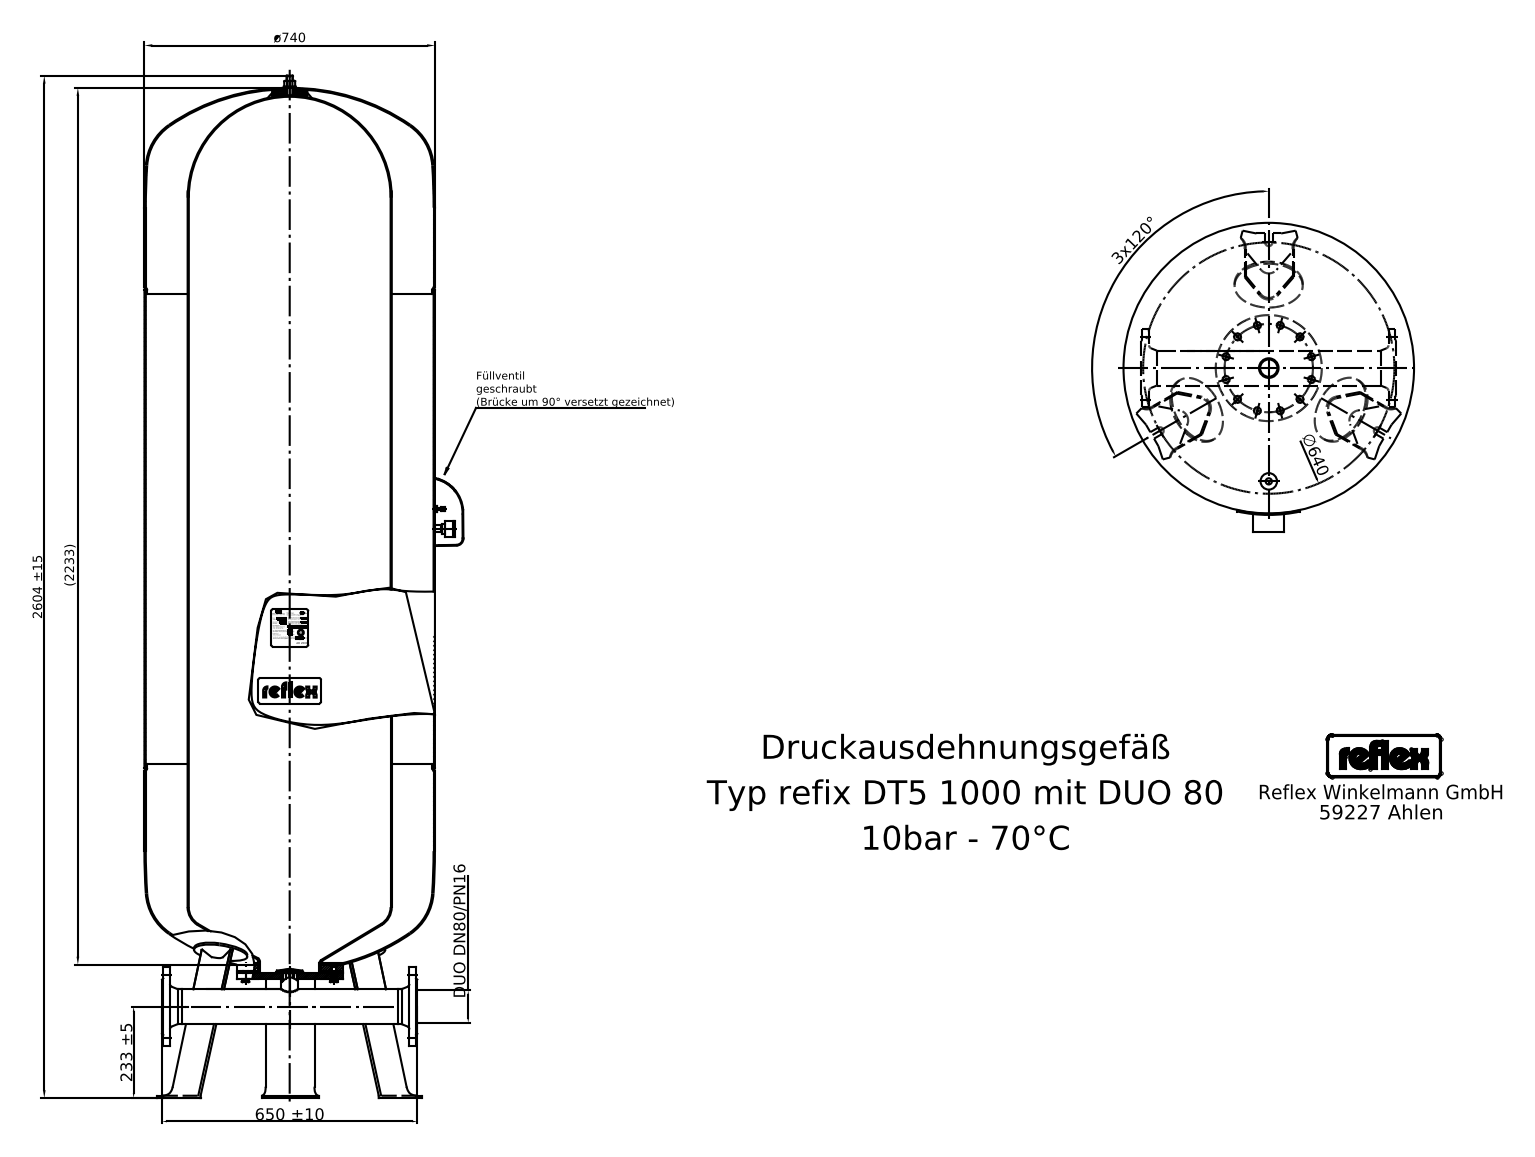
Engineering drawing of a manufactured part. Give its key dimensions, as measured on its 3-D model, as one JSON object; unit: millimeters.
{"step_written_by": "Mechanical Desktop 2008 (CONFIG_CONTROL_DESIGN)", "units": "millimeters", "bodies": {"solids": 26, "faces": 538, "planar": 233, "cylindrical": 163, "other": 142}, "overall_size": [2604, 810.1, 740], "volume_mm3": 919500000, "surface_area_mm2": 8565000, "round_holes": [[19, 8], [2.48, 1], [3.8, 1], [4.3, 1], [4.4, 1], [5.45, 1], [7, 1], [8, 1], [11.4, 1], [88.9, 1], [157, 1], [250, 1]], "round_bosses_or_shafts": [[10, 9], [740, 1], [260, 1], [230, 1], [200, 1], [62, 1], [42.4, 1], [34, 1]], "partial_cylinders_radius": [[25, 18], [5.62, 4], [2.25, 3], [9, 3], [3.84, 2], [6.75, 2], [8, 2], [9.27, 2]], "face_to_face_distances": [1872, 6, 195, 2067, 5.97, 5.89, 201, 2073, 311, 5], "hole_center_spacings": [80, 113.13, 61.22, 61.24, 147.81, 147.82, 160, 50]}
